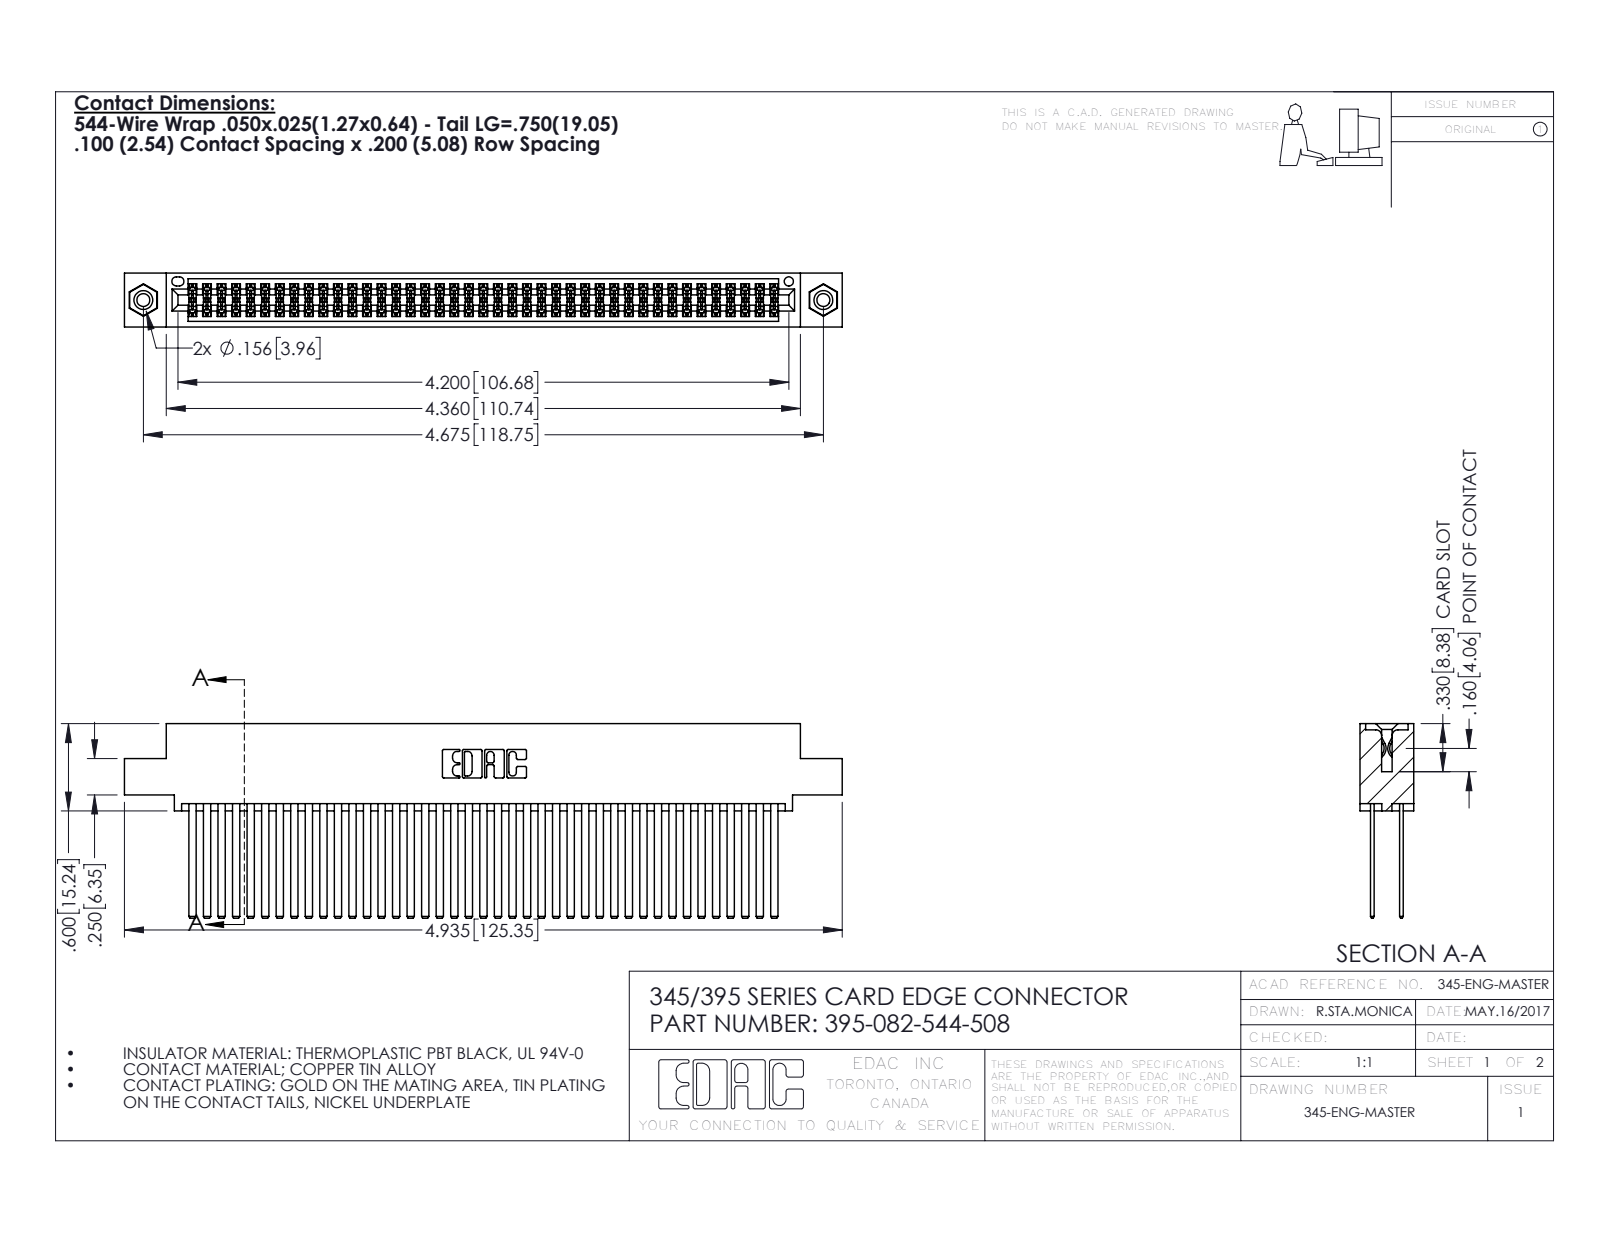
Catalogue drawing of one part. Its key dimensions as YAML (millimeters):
part_name: "345-292-001_345-293-144; 395-082-544-508; 345-250-001_345-250-003-102; 345 Part_0.110 Offset - 0.156 Dia-TI"
step_written_by: "SolidWorks 2016 (CONFIG_CONTROL_DESIGN)"
units: millimeters
bodies: {solids: 85, faces: 3798, planar: 2494, cylindrical: 1288, other: 16}
overall_size: [125.3, 34, 9.4]
volume: 13200
surface_area: 23020
round_holes:
  - {diameter: 2.3, count: 2}
  - {diameter: 3.2, count: 2}
  - {diameter: 4, count: 2}
  - {diameter: 1.6, count: 1}
round_bosses_or_shafts:
  - {diameter: 3.9, count: 2}
partial_cylinders:
  - {radius: 0.2, count: 123}
  - {radius: 0.3, count: 22}
  - {radius: 0.2, count: 6}
  - {radius: 0.8, count: 6}
  - {radius: 0.7, count: 3}
  - {radius: 0.4, count: 2}
  - {radius: 0.5, count: 2}
  - {radius: 0.6, count: 2}
face_to_face_distances: [5.1, 0.6, 1.8, 2.5, 6.9, 7.6, 5.7, 4.4, 9.4, 1.3]
hole_center_spacings: [6.9, 112.8, 118.7]
